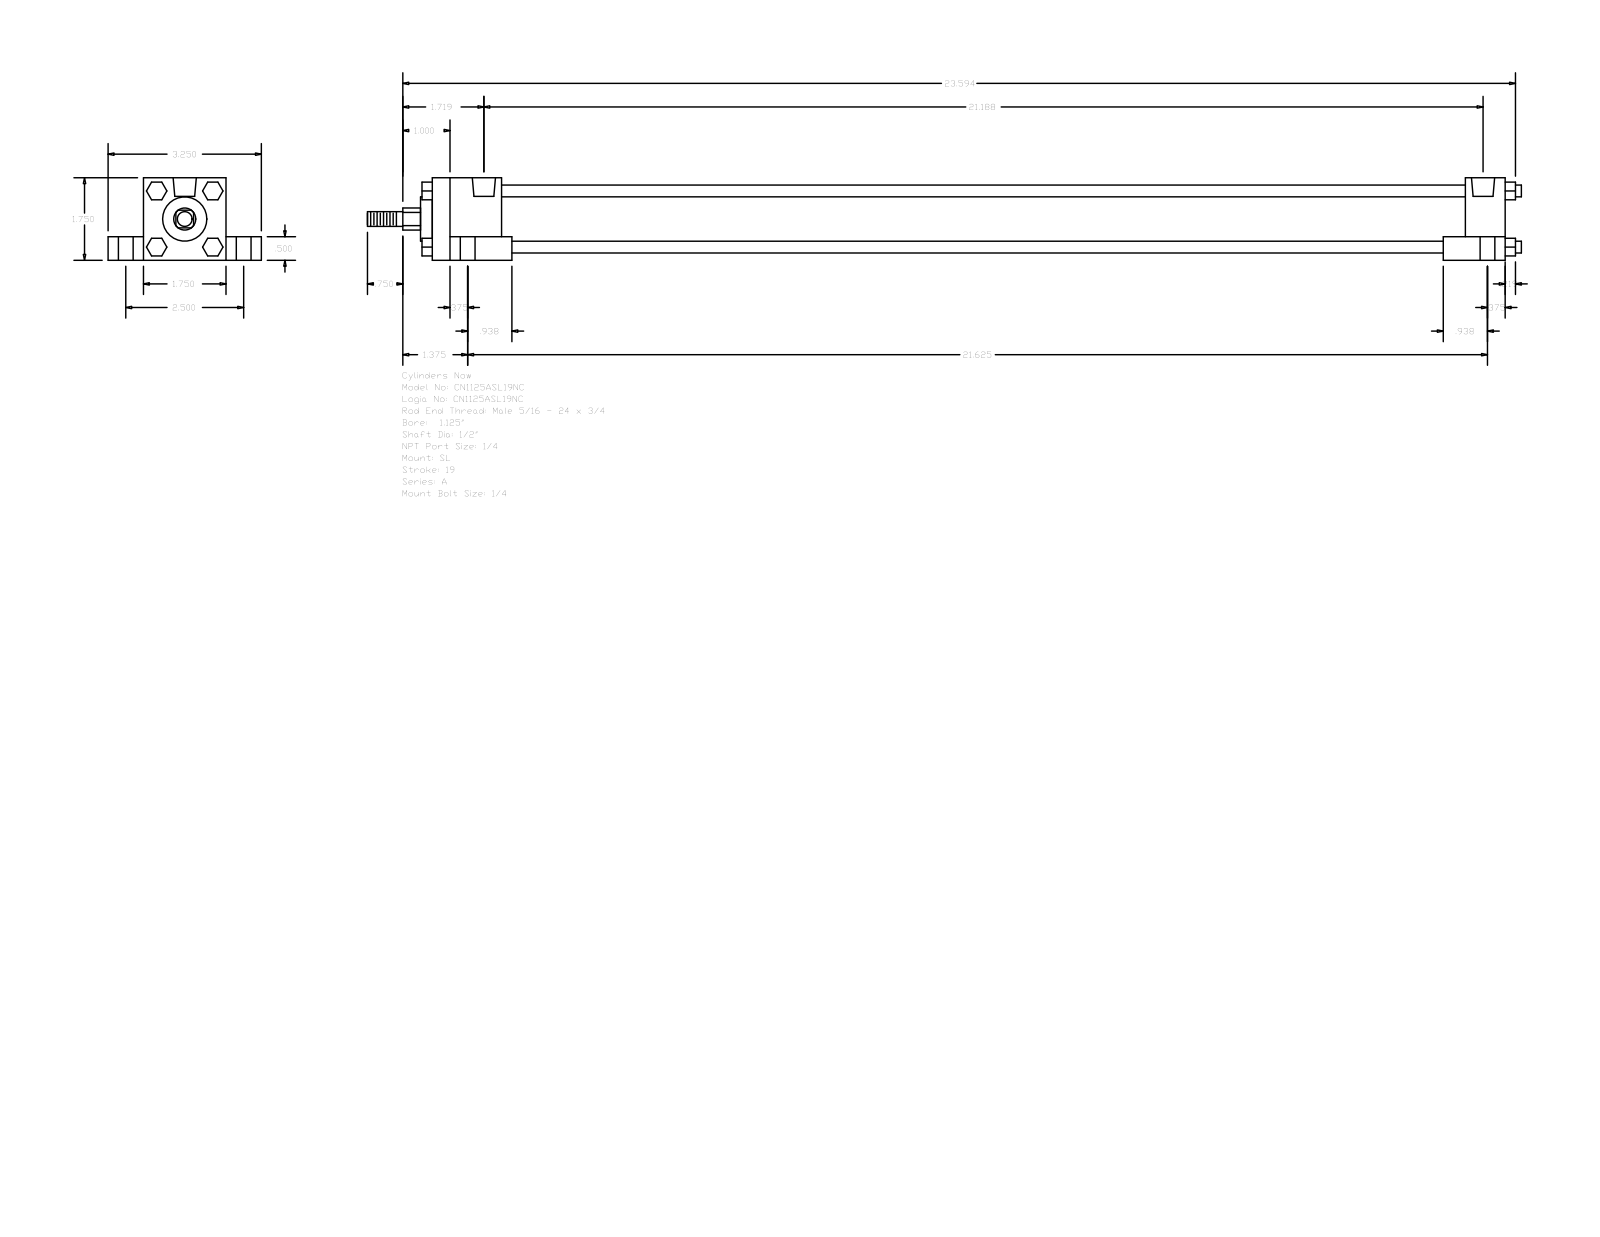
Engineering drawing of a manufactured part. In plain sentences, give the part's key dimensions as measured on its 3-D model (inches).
The part is named "A_SL__0112_0.5". Its 3-D file was written by "GSSL Pune (CONFIG_CONTROL_DESIGN)". It is 0 solids with 150 faces: 114 planar, 36 cylindrical and 0 other. Overall it measures 24.469 by 3.25 by 1.75 inches. Round holes: 4 of diameter 0.219, 4 of diameter 0.313, 4 of diameter 0.563, 2 of diameter 0.492. Round bosses or shafts: 4 of diameter 0.25, 1 of diameter 1.255, 1 of diameter 0.937, 1 of diameter 0.5, 1 of diameter 0.313. Partial cylindrical surfaces (rounded edges, fillets, slot ends): 1 of radius 0.234. The main face-to-face distances are 1.75, 1.25, 0.5, 0.75, 2.5, 22.75, 21.906, 0.844, 1.469, 20.437. The hole center spacings are 1.254, 1.26, 1.296, 1.315, 2.5, 21.063, 21.256, 21.318.
